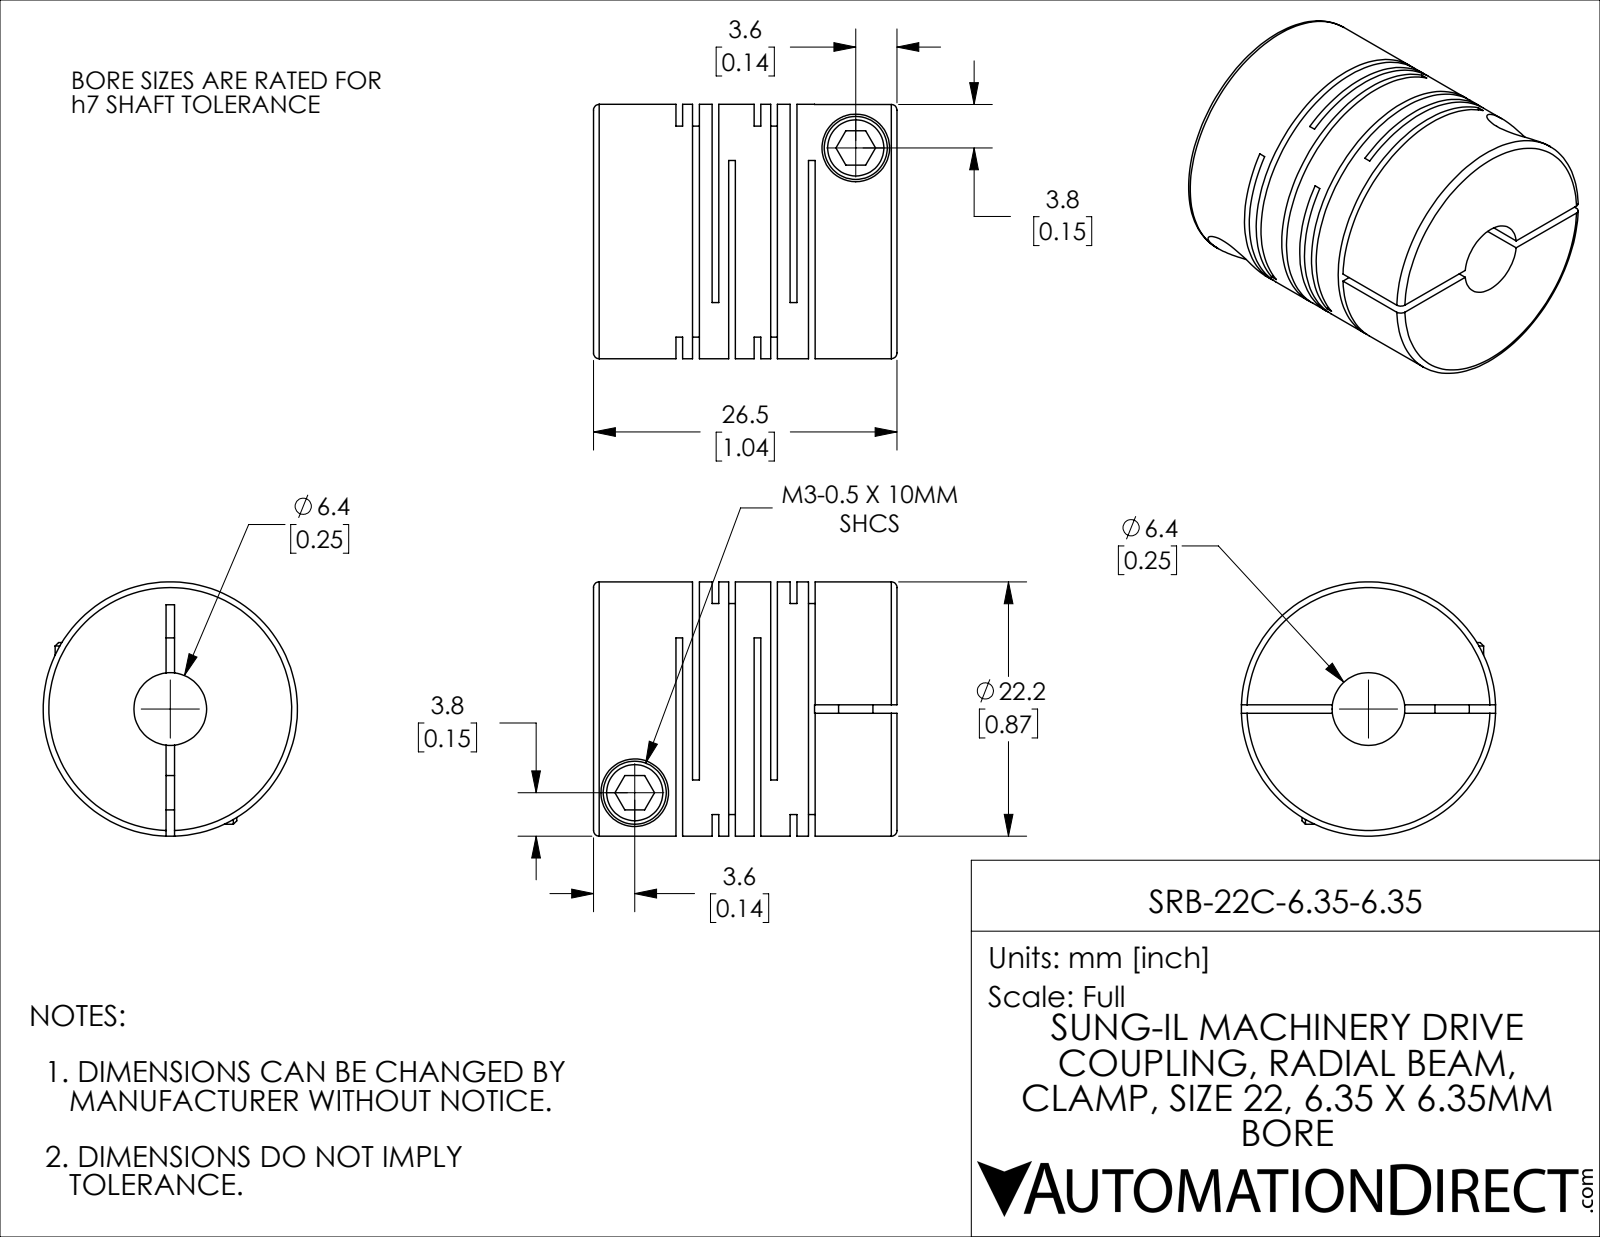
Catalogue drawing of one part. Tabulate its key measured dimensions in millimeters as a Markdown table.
| quantity | value |
| --- | --- |
| part name | SRB-22C-6.35-6.35 |
| STEP written by | SolidWorks 2021 (CONFIG_CONTROL_DESIGN) |
| units | millimeters |
| bodies | 1 solid, 115 faces (60 planar, 42 cylindrical, 13 other) |
| overall size | 26.5 × 22.2 × 22.2 |
| volume | 7 698 mm³ |
| surface area | 8 124 mm² |
| round holes (diameter × count) | 3 × 2, 5.9 × 2, 6.35 × 1 |
| round bosses / shafts (diameter × count) | 5.5 × 2, 22.2 × 1 |
| main face-to-face distances | 0.59, 6.82, 1.45, 3.15, 5.37, 1.7, 3.67, 6.23, 0.86, 2.56 |
